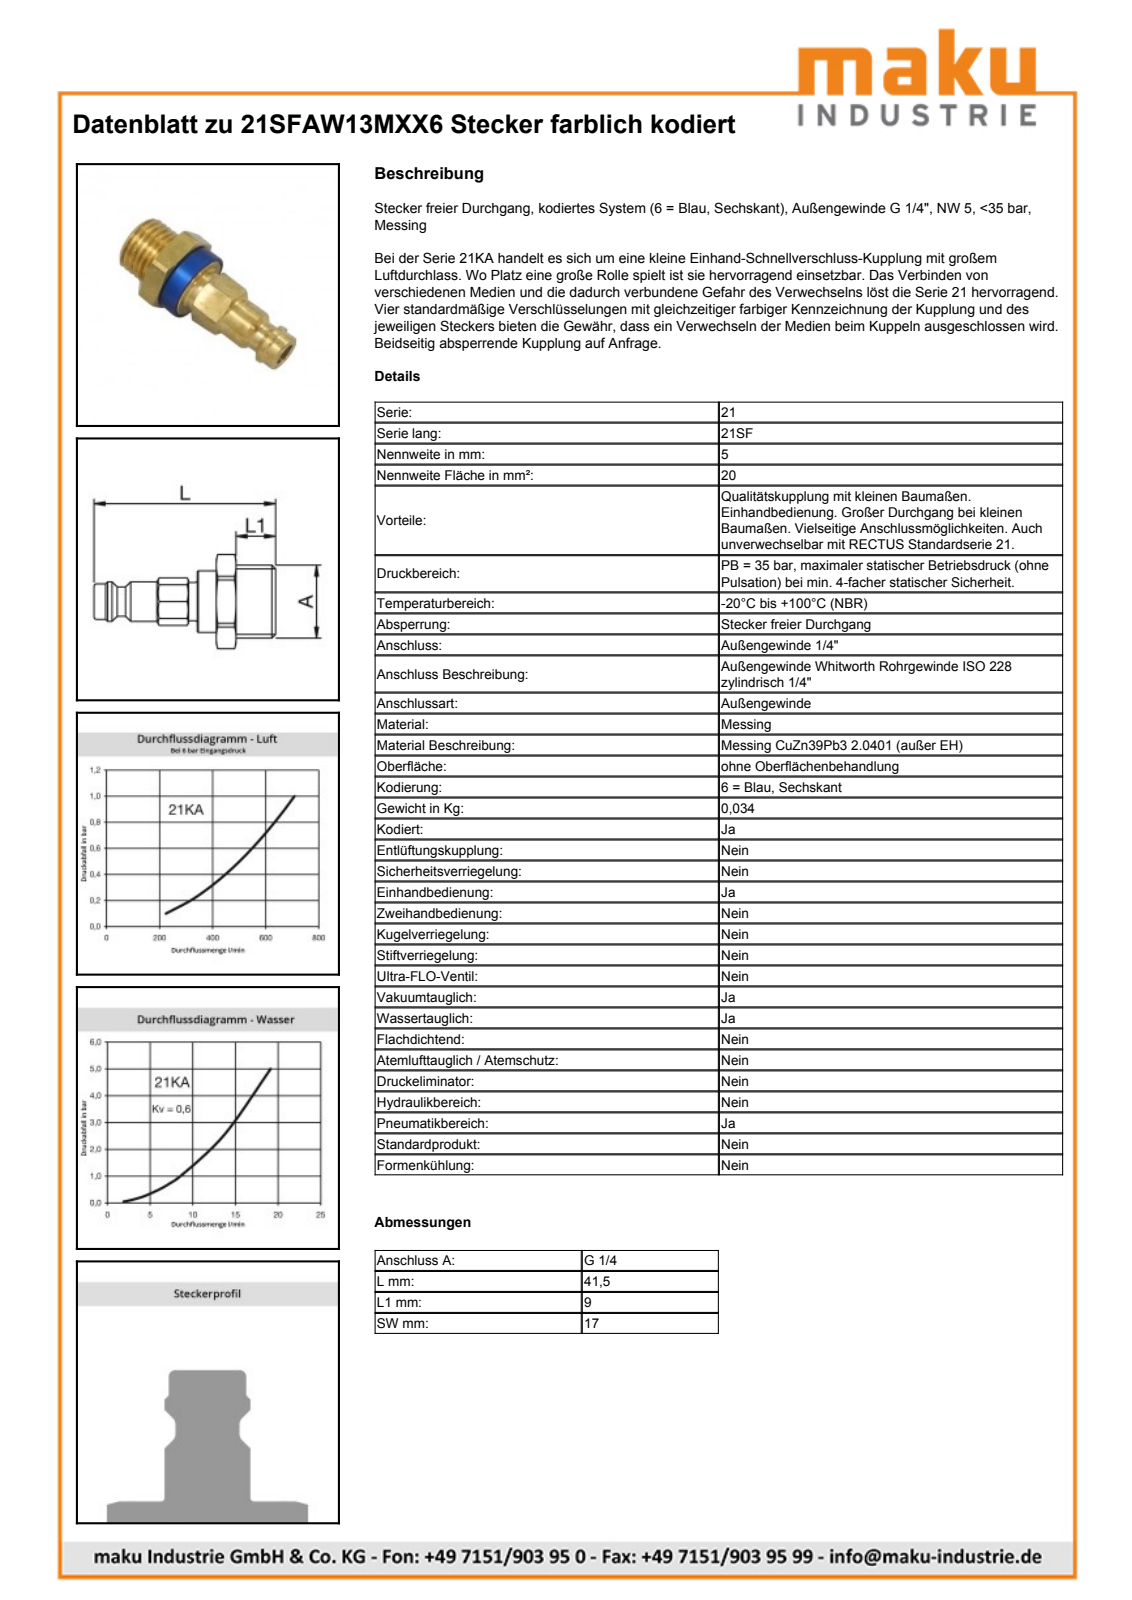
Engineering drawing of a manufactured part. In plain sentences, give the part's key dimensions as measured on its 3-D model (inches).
The part is named "D110186; D110185; D104771". Its 3-D file was written by "Autodesk Inventor 2013 (AUTOMOTIVE_DESIGN)". It is 2 solids with 69 faces: 19 planar, 23 cylindrical and 27 other. Overall it measures 1.634 by 0.748 by 0.669 inches. Its volume is 0.231 cubic inches and its surface area 4.69 square inches. Round holes: 1 of diameter 0.195, 1 of diameter 0.545, 1 of diameter 0.553. Round bosses or shafts: 1 of diameter 0.61, 1 of diameter 0.551, 1 of diameter 0.518, 1 of diameter 0.382, 1 of diameter 0.354, 1 of diameter 0.319, 1 of diameter 0.262. Partial cylindrical surfaces (rounded edges, fillets, slot ends): 1 of radius 0.224, 1 of radius 0.374. The main face-to-face distances are 0.531, 0.138, 0.177, 0.669, 0.394, 0.354, 0.709, 0.165, 0.343, 0.697.
